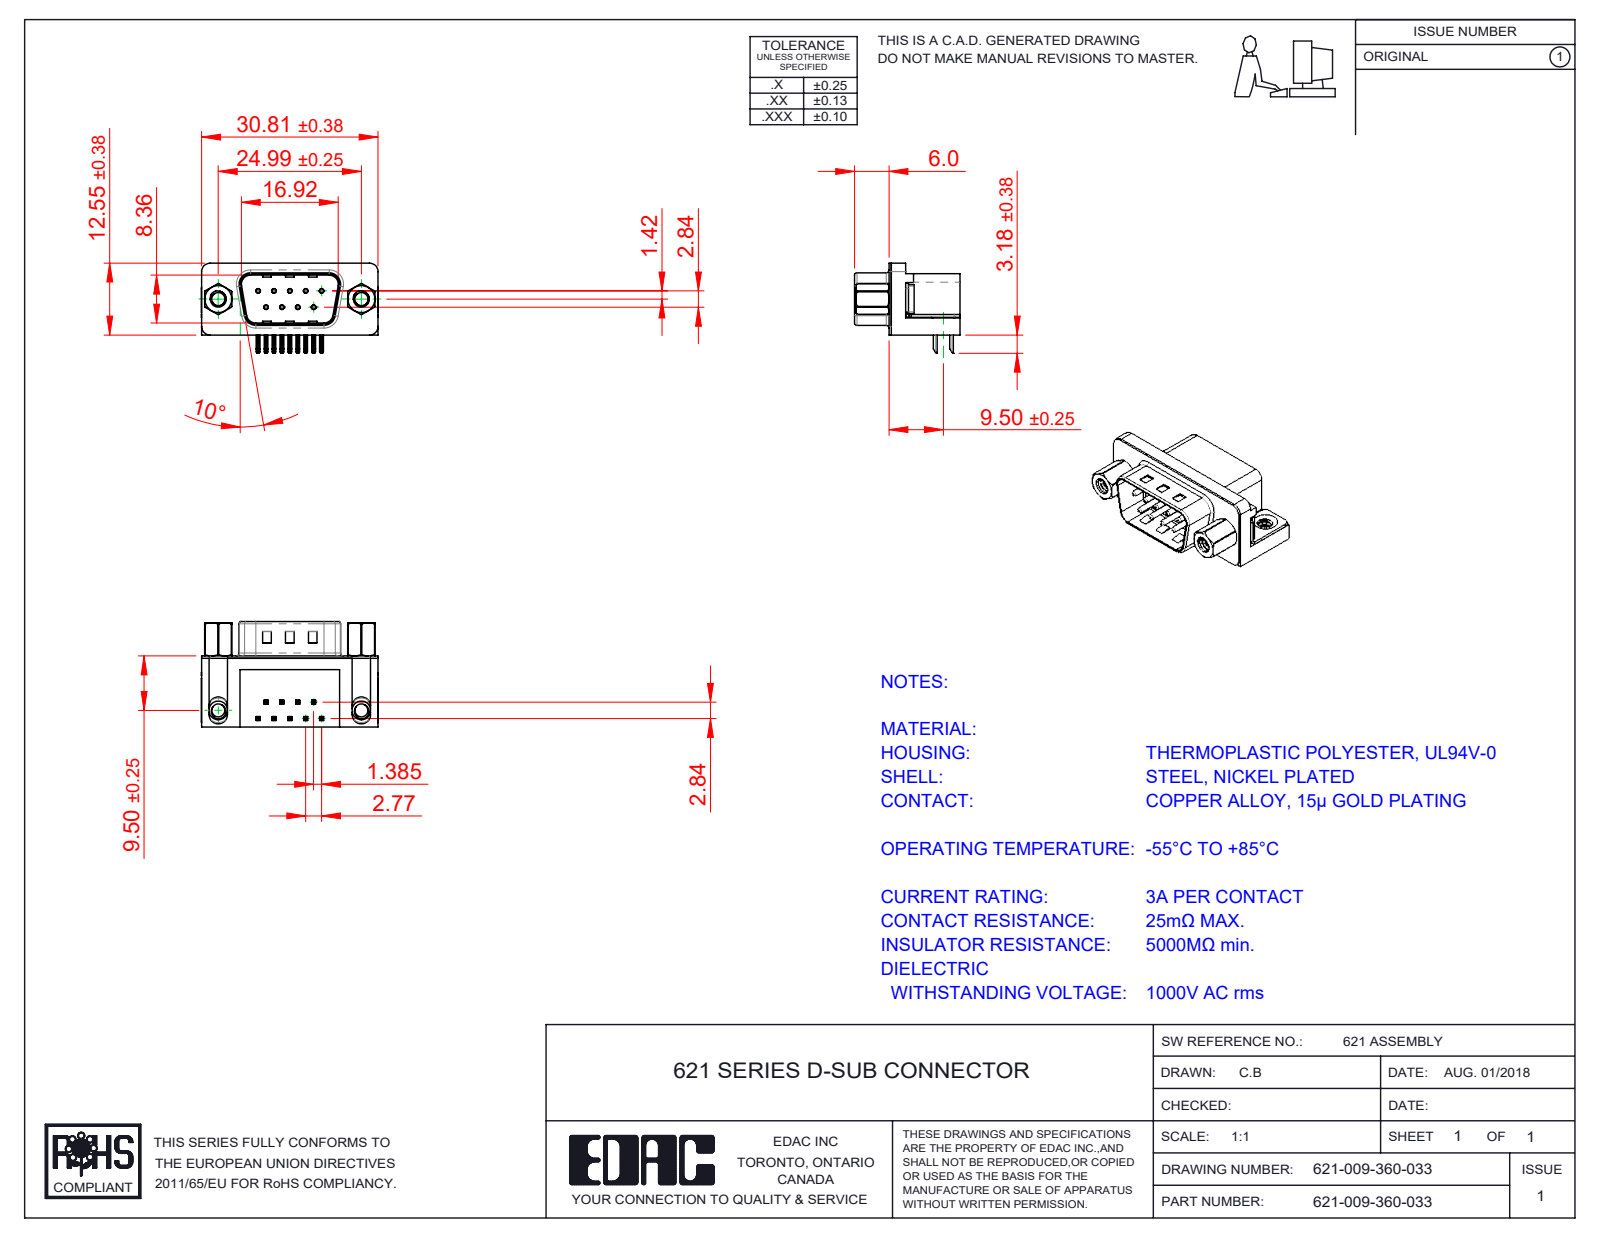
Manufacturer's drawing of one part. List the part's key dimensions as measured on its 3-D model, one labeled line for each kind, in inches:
Part name (STEP PRODUCT): 621 Housing_9 Socket; 621-009-360-033; 621 4-40 Hex Standoff 5; 621 Contact Bottom (+4 more)
STEP written by: SolidWorks 2016 (CONFIG_CONTROL_DESIGN)
Units: inches
Bodies: 17 solids, 1157 faces (627 planar, 395 cylindrical, 135 other)
Overall size (bounding box): 1.216 × 0.724 × 0.64
Volume: 0.211 in³ · Surface area: 7.609 in²
Round holes (diameter × count): ⌀0.014 ×9, ⌀0.031 ×9, ⌀0.089 ×2, ⌀0.09 ×2, ⌀0.157 ×2, ⌀0.189 ×2, ⌀0.197 ×2
Round bosses / shafts (diameter × count): ⌀0.03 ×9, ⌀0.193 ×2, ⌀0.187 ×2, ⌀0.154 ×2, ⌀0.11 ×2
Partial cylindrical surfaces — rounded edges, fillets, slot ends (radius × count): R0.01 ×44, R0.005 ×18, R0.039 ×16, R0.02 ×14, R0.059 ×8, R0.063 ×8, R0.013 ×4, R0.035 ×4
Main face-to-face distances: 0.016, 0.472, 0.488, 0.407, 0.02, 0.374, 0.098, 0.114, 0.083, 0.014
Hole centre spacings: 0.124, 0.109, 0.218, 0.198, 0.198, 0.327, 0.294, 0.295
